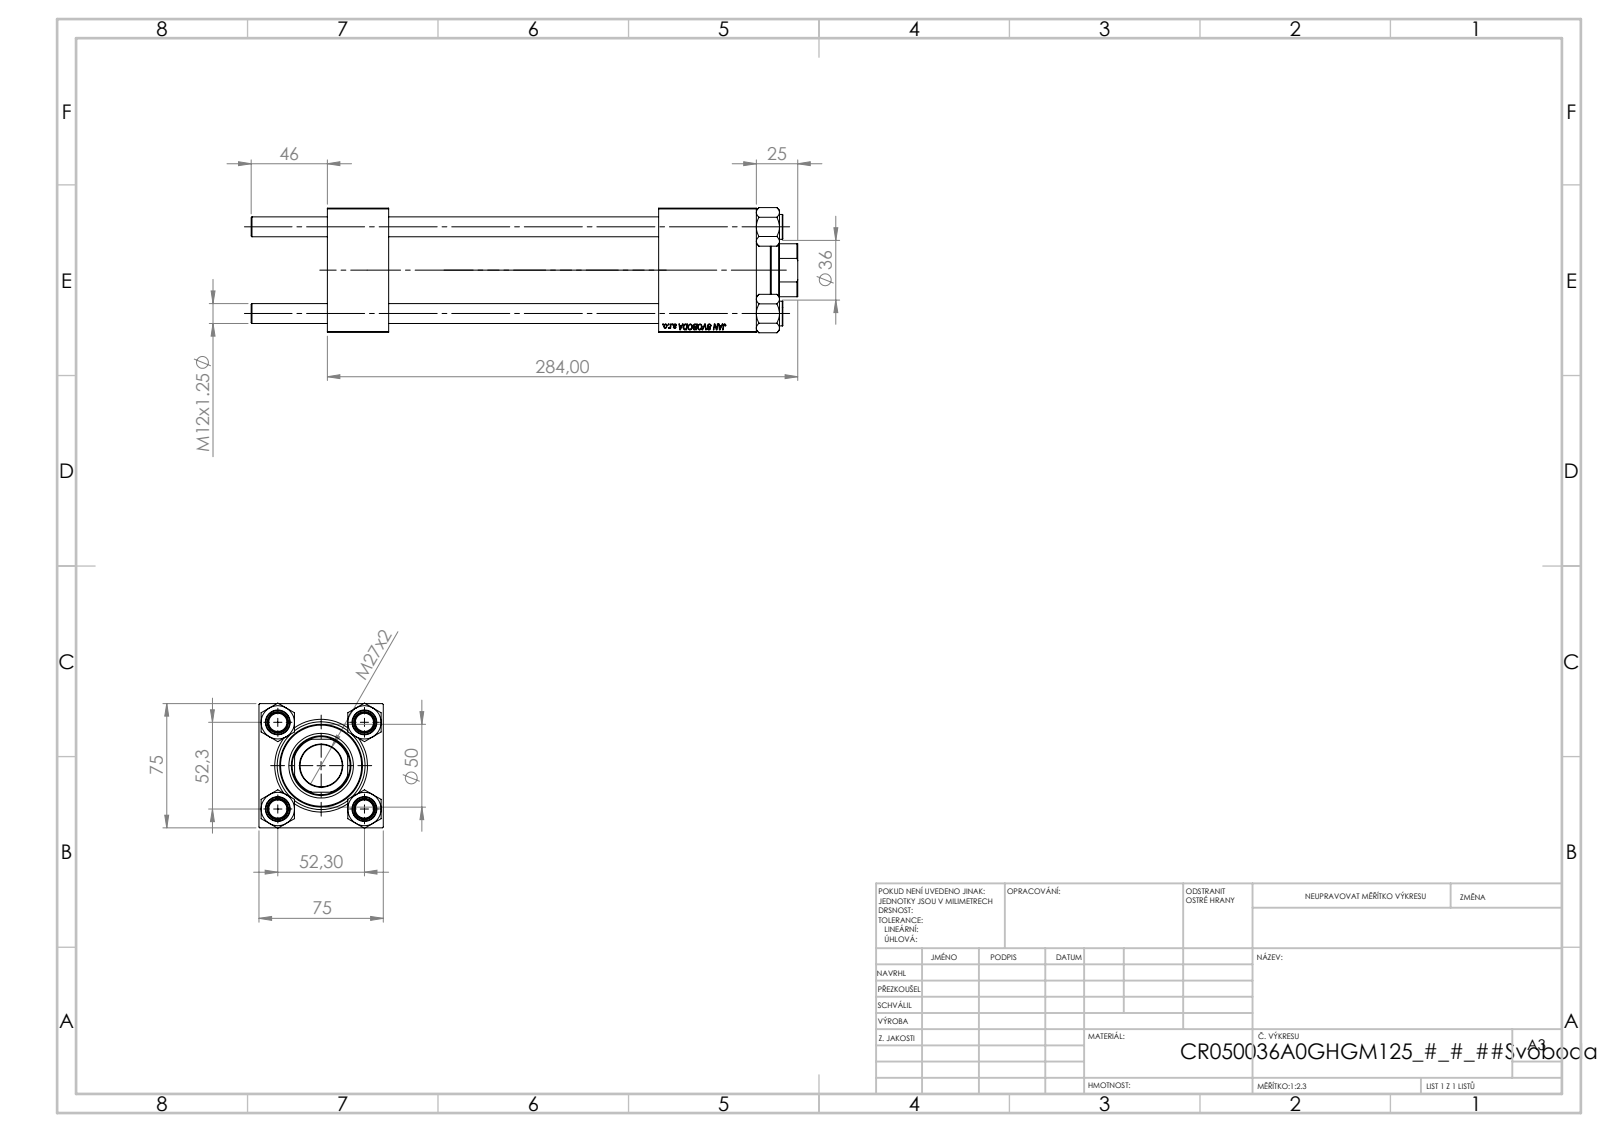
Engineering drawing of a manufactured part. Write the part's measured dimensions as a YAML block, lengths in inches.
part_name: "V215CR_VCP; V215CR_BODY_A; CR025_012_A_0_G_A_G_M_020_+#_##_TYCINKA; NUT_M5 (+1 more)"
step_written_by: "SolidWorks 2019 (CONFIG_CONTROL_DESIGN)"
units: inches
bodies: {solids: 11, faces: 1134, planar: 520, cylindrical: 78, other: 536}
overall_size: [12.992, 2.974, 2.953]
volume: 56.51
surface_area: 363.7
round_holes:
  - {diameter: 0.472, count: 4}
  - {diameter: 0.276, count: 2}
  - {diameter: 0.825, count: 2}
  - {diameter: 1.181, count: 2}
  - {diameter: 1.004, count: 1}
  - {diameter: 1.417, count: 1}
  - {diameter: 1.535, count: 1}
  - {diameter: 1.614, count: 1}
  - {diameter: 2.087, count: 1}
round_bosses_or_shafts:
  - {diameter: 0.591, count: 4}
  - {diameter: 2.205, count: 1}
  - {diameter: 1.969, count: 1}
partial_cylinders:
  - {radius: 0.689, count: 1}
face_to_face_distances: [2.953, 1.457, 7.874, 10.197, 8.74, 6.417, 2.323, 9.067, 7.61, 1.193]
hole_center_spacings: [1.456, 2.059, 2.912, 7.815]
